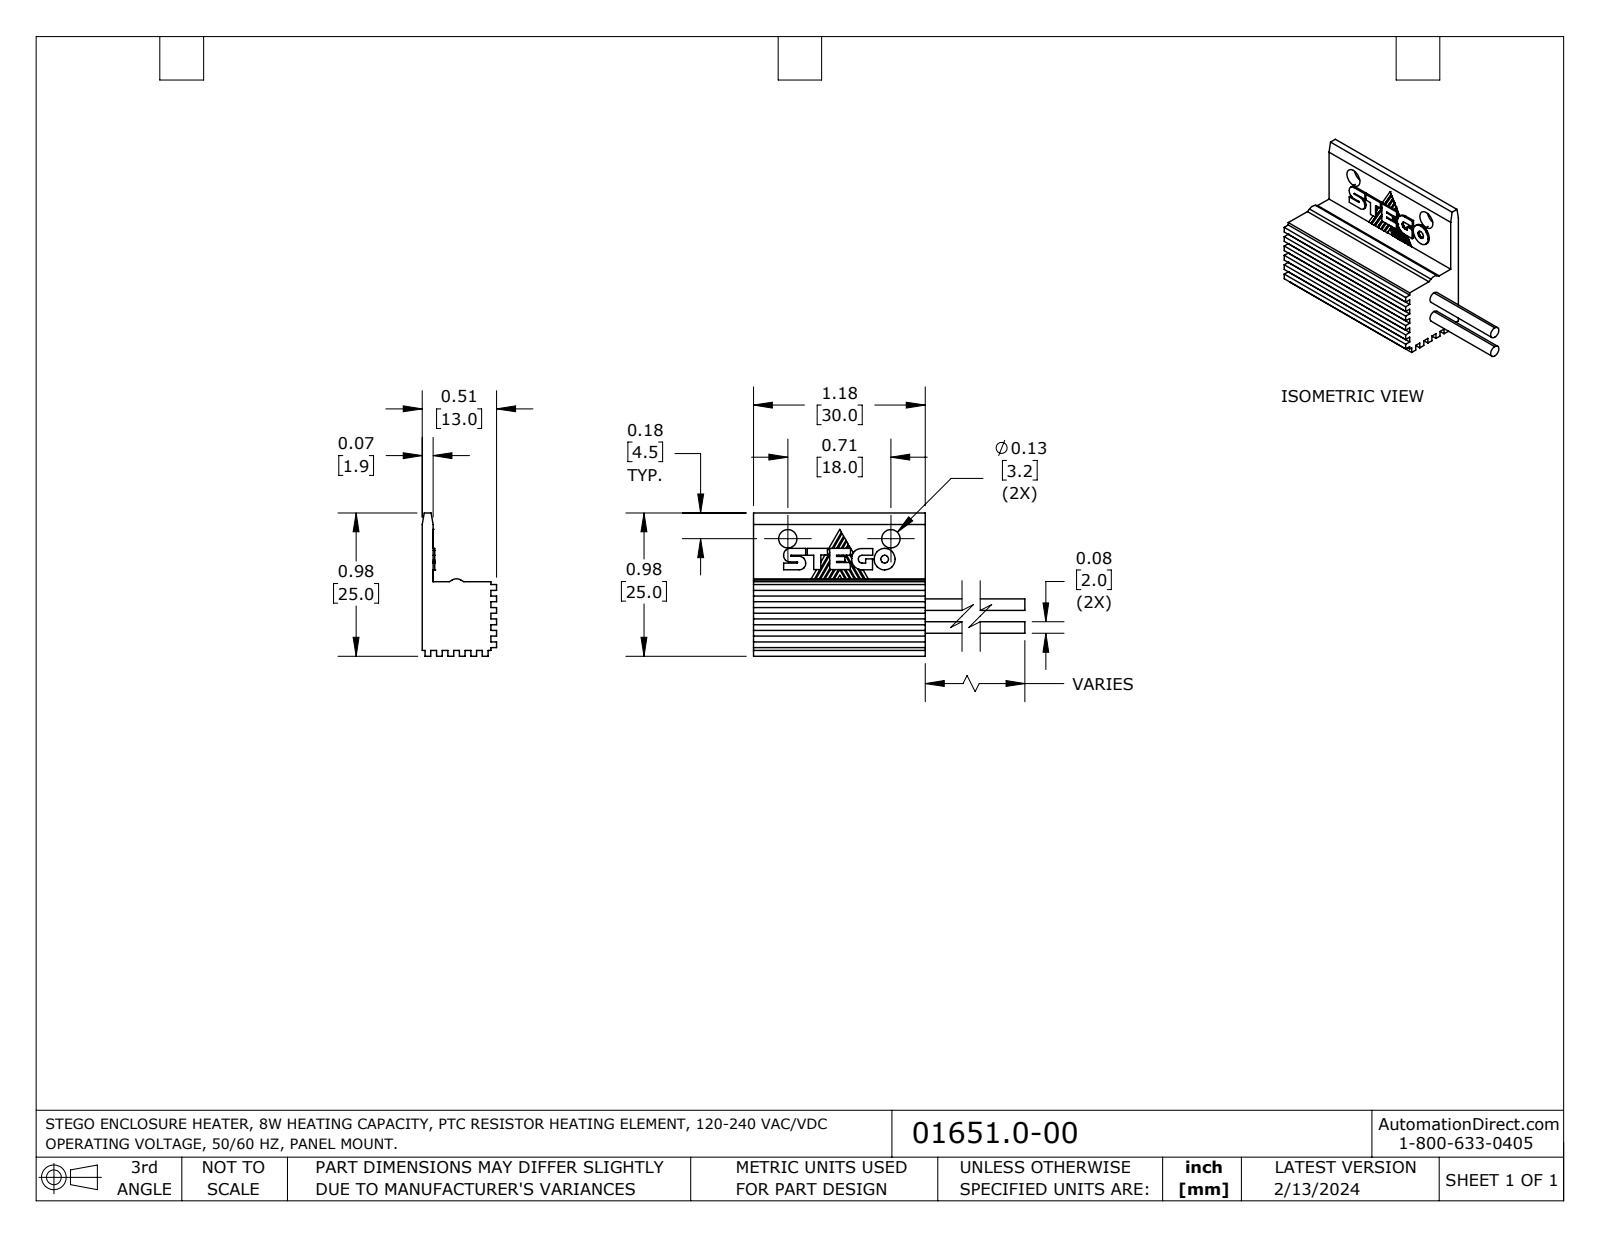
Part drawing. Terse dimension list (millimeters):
name: RC_016_30mm_EPLAN_08_2022
written by: SolidWorks 2022 (AUTOMOTIVE_DESIGN)
unit: mm
bodies: 1 solid, 252 faces (193 planar, 13 cylindrical, 46 other)
size: 45 × 25 × 13
volume: 5 455 mm³; area: 3 471 mm²
holes: 2× ⌀3.2
bosses: 2× ⌀2
rounds: 1× R1.5, 1× R1.83, 1× R2.03
face distances: 1, 2, 3, 4, 5, 12, 13, 6, 7, 8
hole spacings: 18
